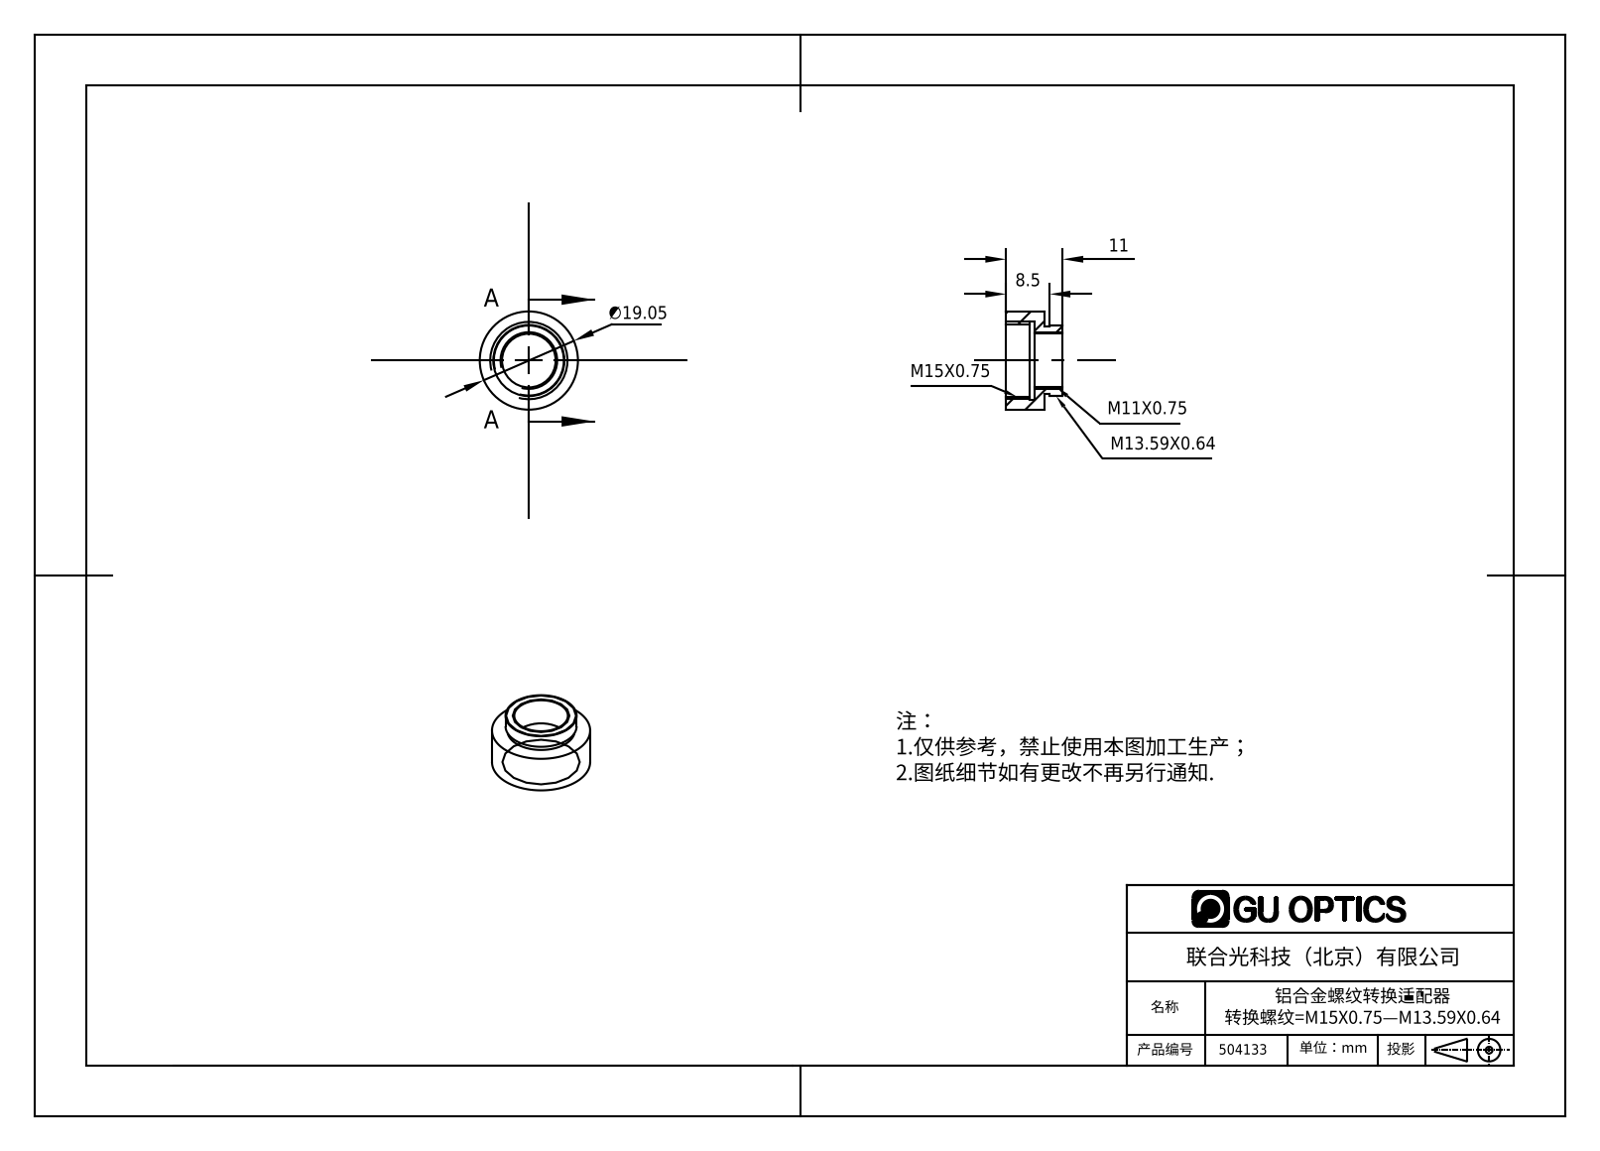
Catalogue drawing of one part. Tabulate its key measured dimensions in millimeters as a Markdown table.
| quantity | value |
| --- | --- |
| part name | 504133 |
| STEP written by | SolidWorks 2016 (AUTOMOTIVE_DESIGN) |
| units | millimeters |
| bodies | 1 solid, 18 faces (6 planar, 12 cylindrical, 0 other) |
| overall size | 19.05 × 19.05 × 11 |
| volume | 1 305 mm³ |
| surface area | 1 509 mm² |
| round holes (diameter × count) | 10.4 × 1, 14 × 1, 15.2 × 1 |
| round bosses / shafts (diameter × count) | 19.05 × 1, 13.8 × 1, 13.1 × 1 |
| main face-to-face distances | 5.5, 7.5, 2, 11, 3.5, 1, 3, 4.5, 6.5, 8.5 |
